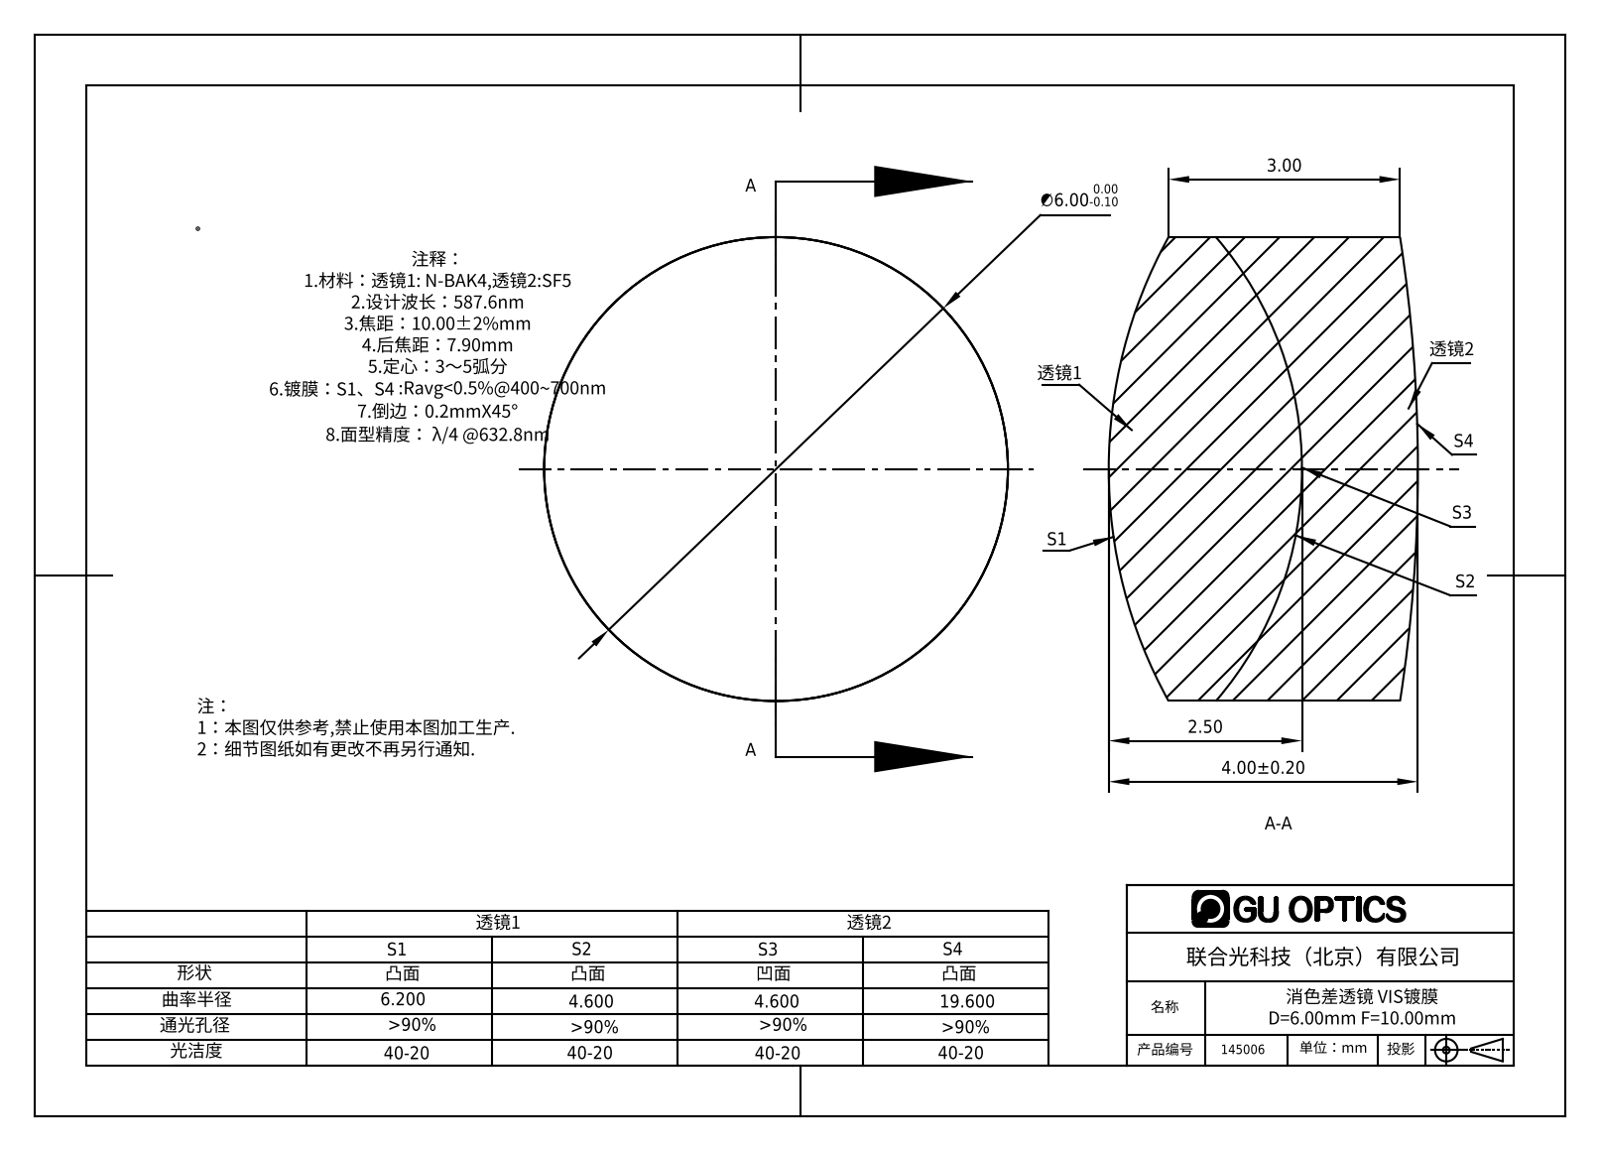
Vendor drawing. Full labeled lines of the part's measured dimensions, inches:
Part name (STEP PRODUCT): 145006
STEP written by: SolidWorks 2016 (AUTOMOTIVE_DESIGN)
Units: inches
Bodies: 2 solids, 12 faces (0 planar, 4 cylindrical, 8 other)
Overall size (bounding box): 0.236 × 0.236 × 0.157
Volume: 0.006 in³ · Surface area: 0.277 in²
Round bosses / shafts (diameter × count): ⌀0.236 ×1
